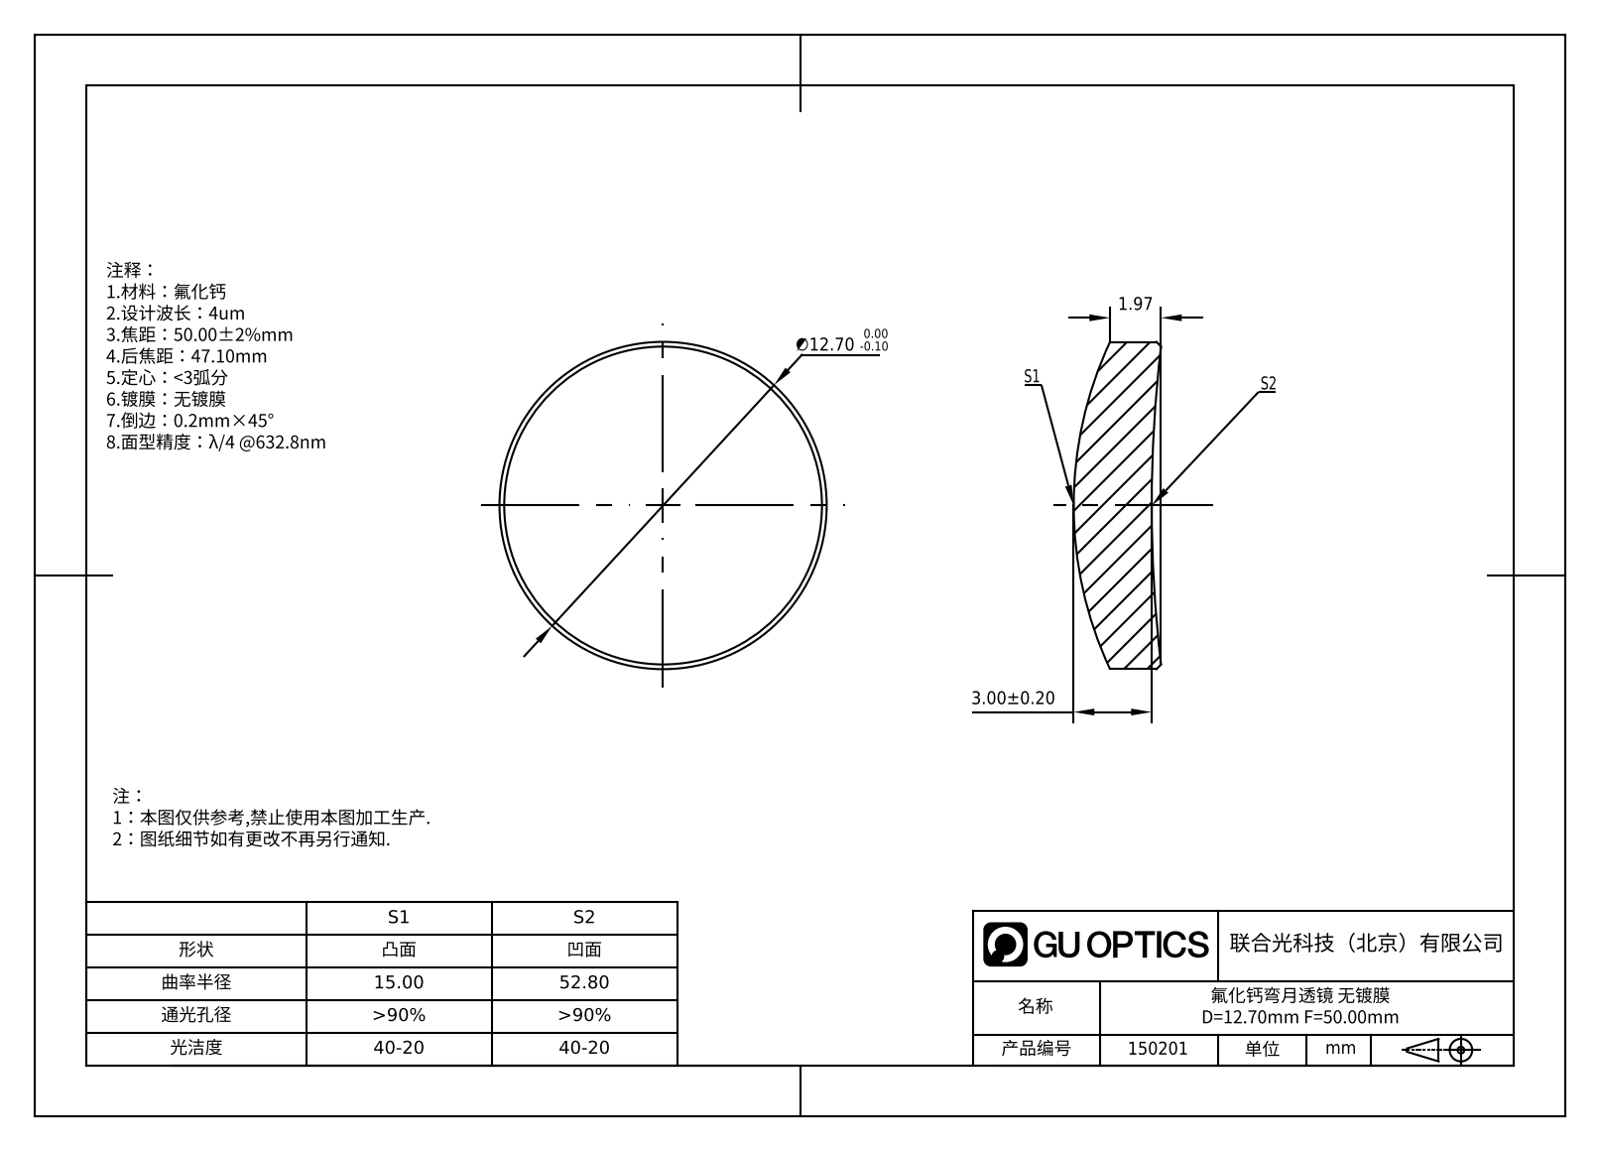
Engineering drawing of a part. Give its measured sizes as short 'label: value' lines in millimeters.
name: GLM5-012B-050
written by: SolidWorks 2022 (AUTOMOTIVE_DESIGN)
unit: mm
bodies: 1 solid, 8 faces (0 planar, 2 cylindrical, 6 other)
size: 12.7 × 12.7 × 3.39
volume: 319 mm³; area: 335 mm²
bosses: 1× ⌀12.7
